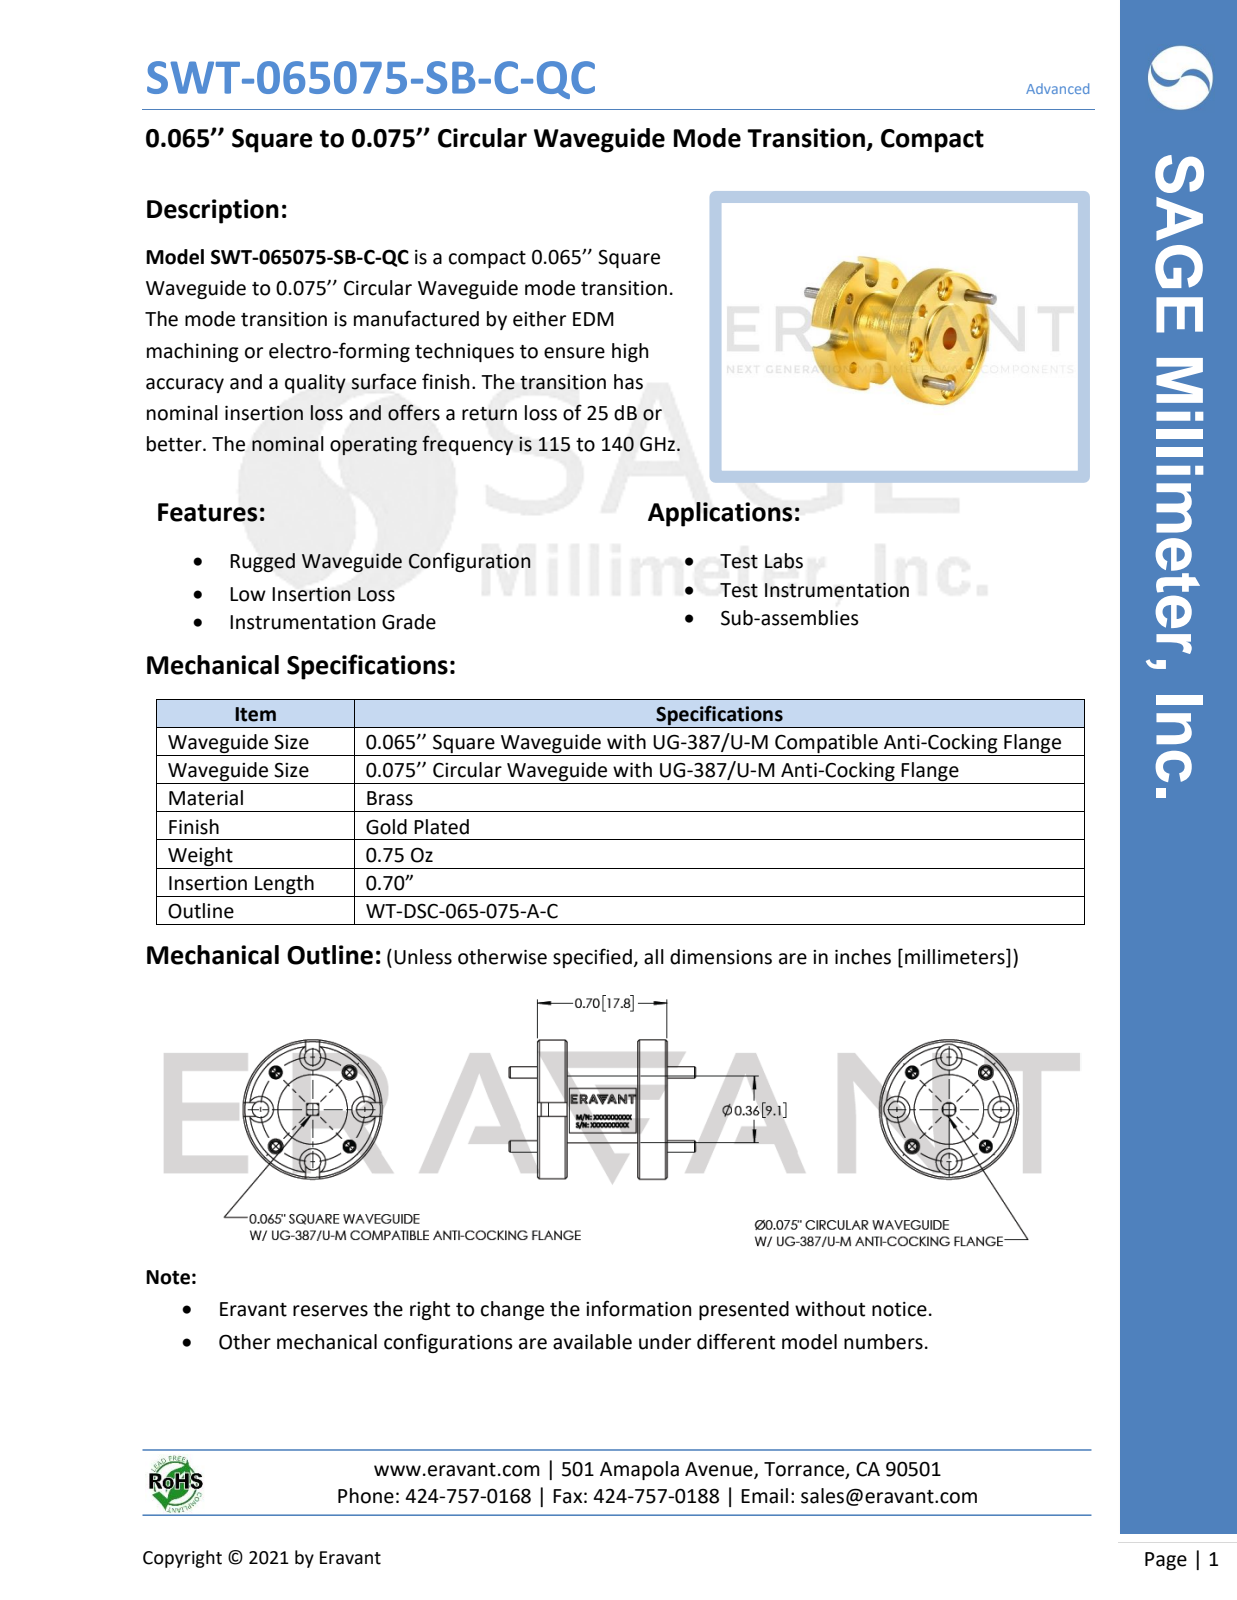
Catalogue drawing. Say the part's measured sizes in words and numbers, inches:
The part is named "WT-DSC-065-075-A-C". Its 3-D file was written by "SolidWorks 2021 (AUTOMOTIVE_DESIGN)". It is 5 solids with 167 faces: 37 planar, 78 cylindrical and 52 other. Overall it measures 1.005 by 0.75 by 0.75 inches. Its volume is 0.157 cubic inches and its surface area 3.452 square inches. Round holes: 4 of diameter 0.061, 4 of diameter 0.067, 4 of diameter 0.089, 4 of diameter 0.14, 1 of diameter 0.68. Round bosses or shafts: 4 of diameter 0.063, 1 of diameter 0.75, 1 of diameter 0.375, 1 of diameter 0.36. The main face-to-face distances are 0.14, 0.52, 0.02, 0.16, 0.54, 0.68, 0.38, 0.66, 0.7, 0.06. The hole center spacings are 0.215, 0.281, 0.398, 0.519, 0.562.
